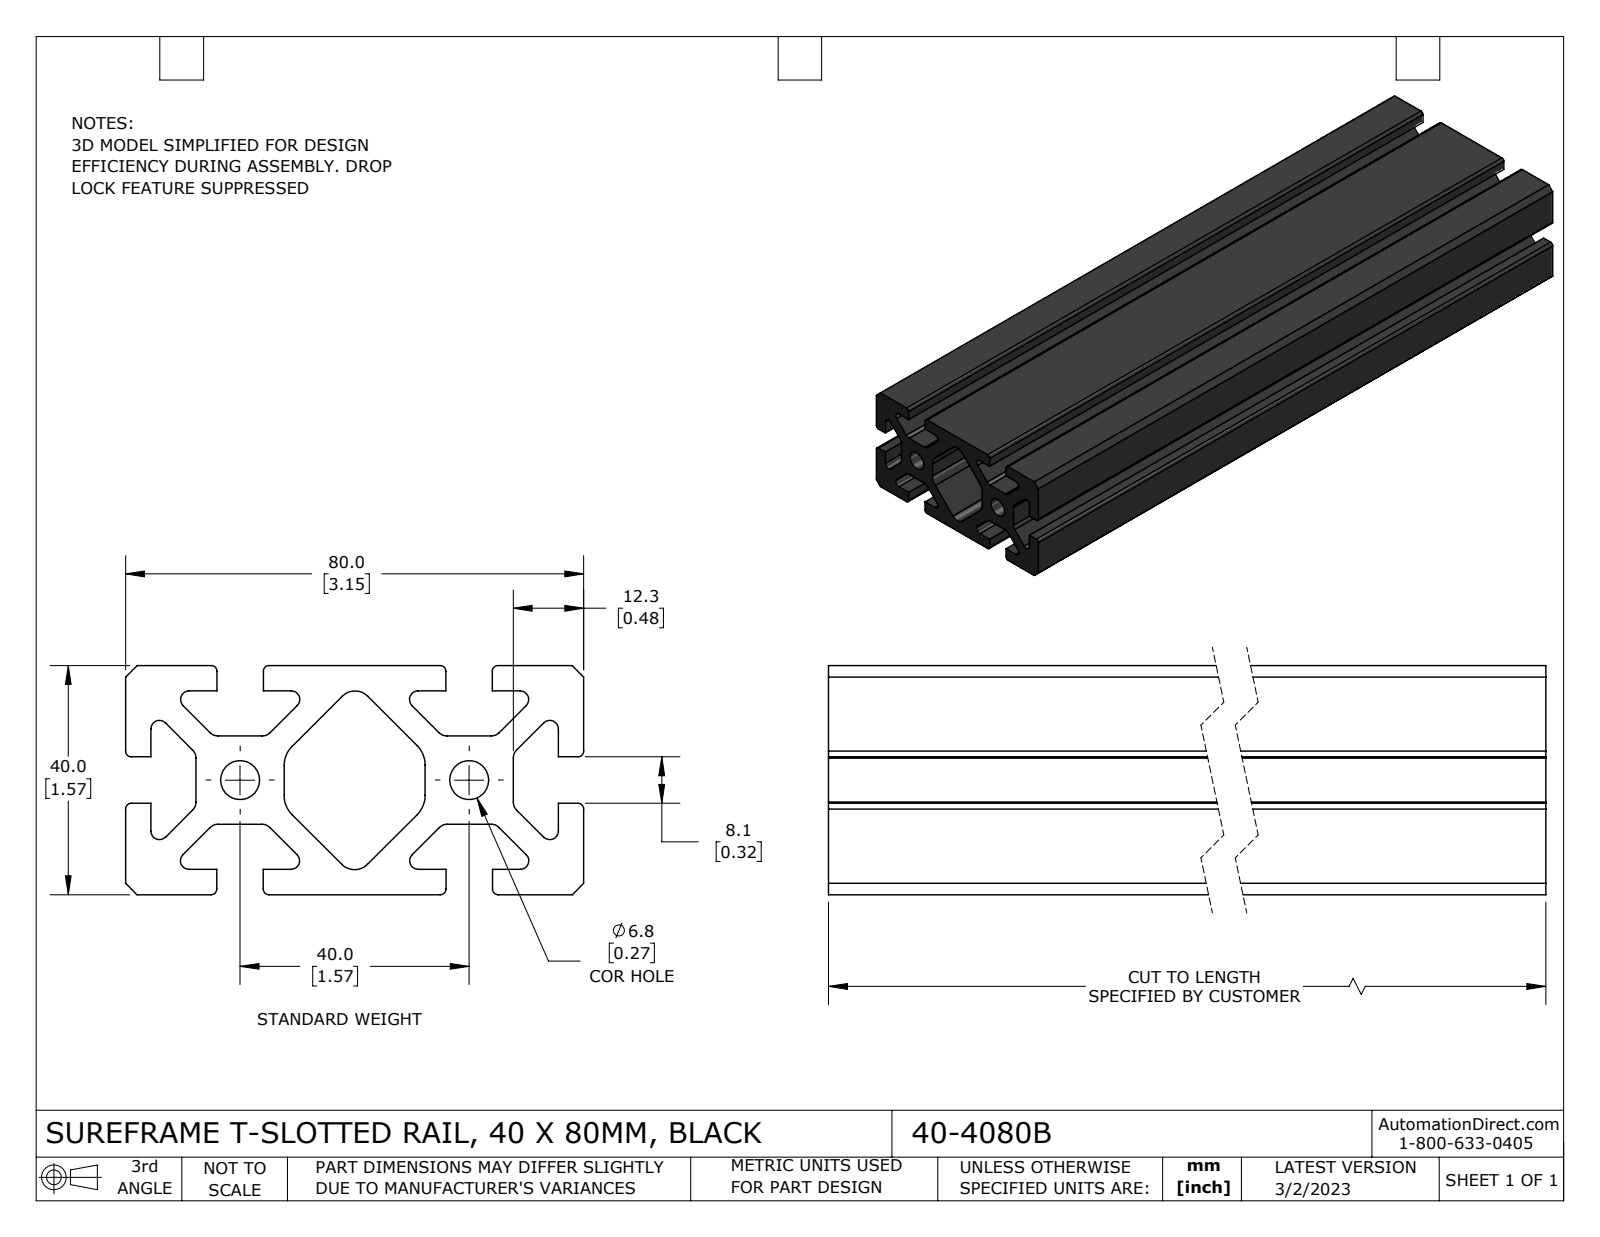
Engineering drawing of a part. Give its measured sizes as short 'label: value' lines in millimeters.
name: 40-4080B
written by: SolidWorks 2021 (CONFIG_CONTROL_DESIGN)
unit: mm
bodies: 1 solid, 116 faces (64 planar, 52 cylindrical, 0 other)
size: 254 × 80 × 40
volume: 406 582 mm³; area: 157 496 mm²
holes: 2× ⌀6.81
rounds: 12× R1, 12× R1.5, 12× R2, 4× R4.75, 2× R3.17
face distances: 40, 4.42, 12.29, 7.87, 35.58, 4.3, 28.28, 27.71, 23.29, 28.26
hole spacings: 40
